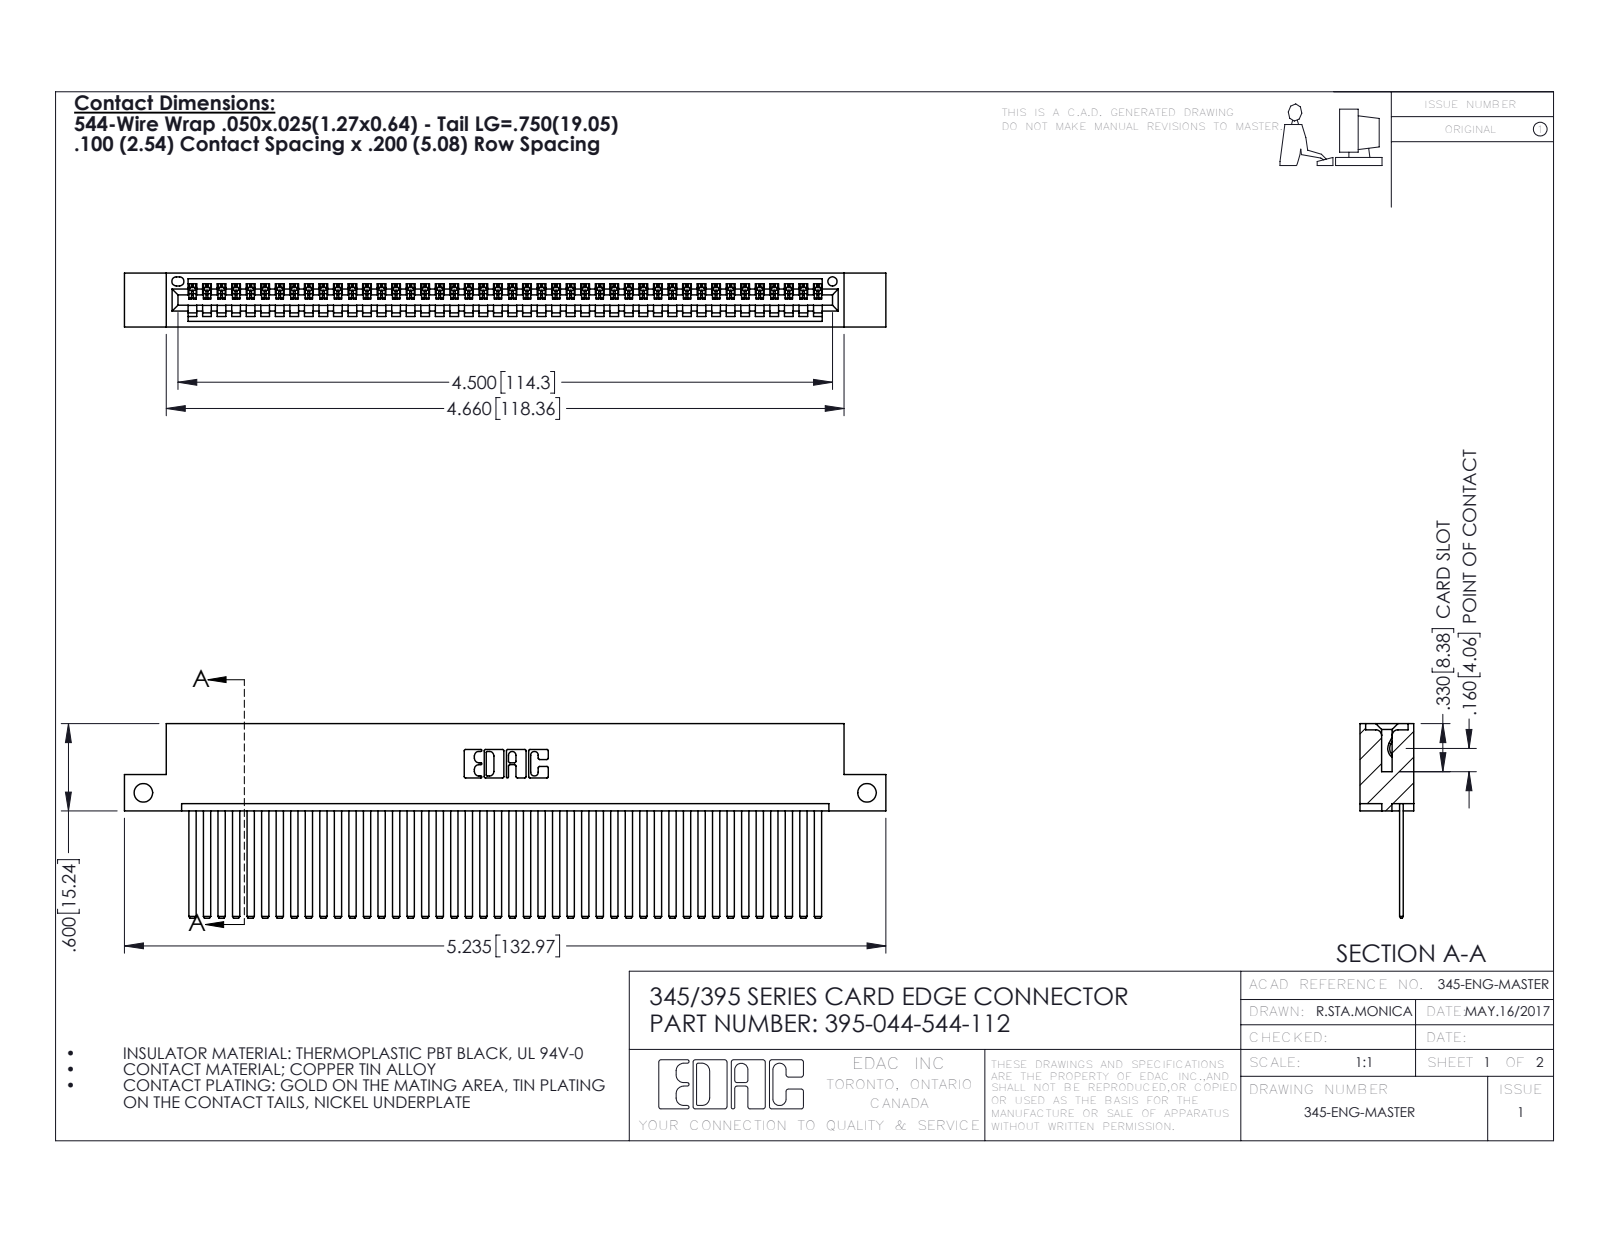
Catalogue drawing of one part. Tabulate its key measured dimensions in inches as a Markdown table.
| quantity | value |
| --- | --- |
| part name | 345 Part_Flush Mounting Lugs - Side Mount; 345-292-001_345-293-144; 395-044-544-112 |
| STEP written by | SolidWorks 2016 (CONFIG_CONTROL_DESIGN) |
| units | inches |
| bodies | 45 solids, 2414 faces (1664 planar, 750 cylindrical, 0 other) |
| overall size | 5.235 × 1.337 × 0.37 |
| volume | 0.797 in³ |
| surface area | 29.11 in² |
| round holes (diameter × count) | 0.128 × 2, 0.064 × 1 |
| partial cylindrical surfaces (radius × count) | 0.006 × 88, 0.01 × 22, 0.007 × 6, 0.031 × 6, 0.026 × 3, 0.031 × 2, 0.04 × 2, 0.014 × 1 |
| main face-to-face distances | 0.072, 0.298, 0.025, 0.098, 0.272, 0.37, 0.2, 0.225, 0.149, 0.072 |
| hole center spacings | 4.975 |
